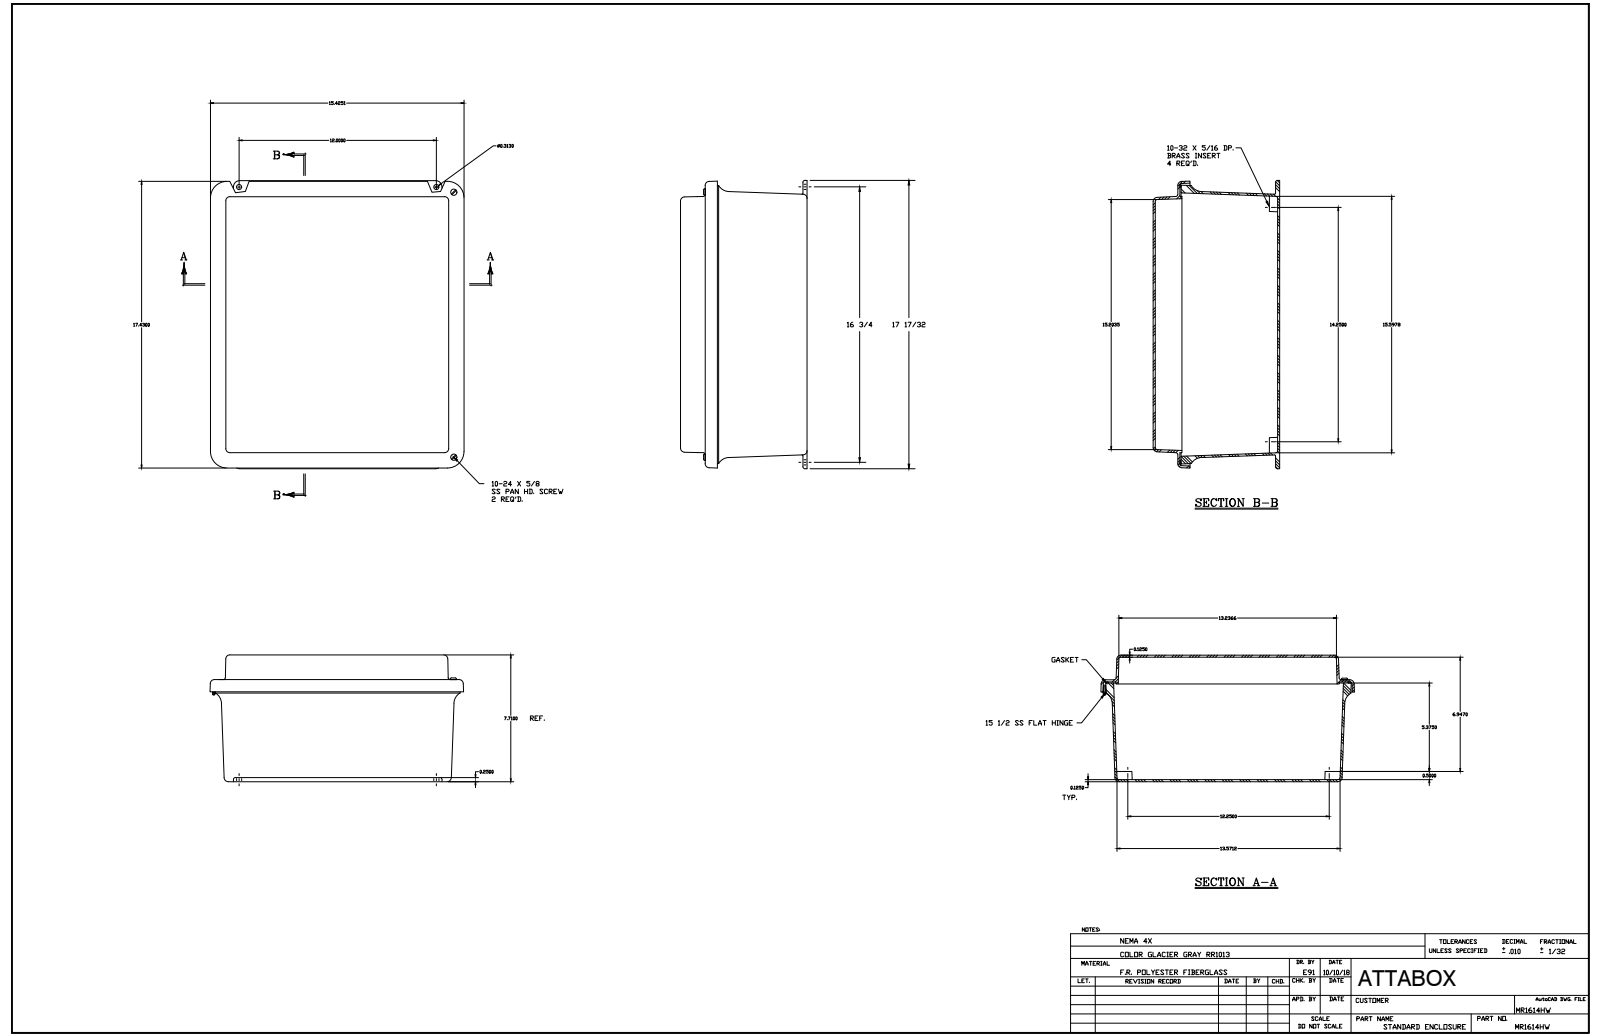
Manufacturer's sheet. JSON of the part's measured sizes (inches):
{"part_name": "MR1614HW", "step_written_by": "SolidWorks 2018 (AUTOMOTIVE_DESIGN)", "units": "inches", "bodies": {"solids": 24, "faces": 965, "planar": 364, "cylindrical": 370, "other": 231}, "overall_size": [17.531, 15.453, 7.697], "volume_in3": 146.7, "surface_area_in2": 2101, "round_holes": [[0.131, 10], [0.14, 10], [0.152, 8], [0.156, 4], [0.218, 4], [0.145, 2], [0.085, 1]], "round_bosses_or_shafts": [[0.25, 10], [0.27, 6], [0.125, 5], [0.125, 5], [0.19, 2], [0.156, 2], [0.155, 1], [0.085, 1]], "partial_cylinders_radius": [[0.031, 20], [0.125, 20], [0.25, 20], [0.2, 4], [0.297, 4], [0.375, 4], [0.75, 4], [0.063, 2]], "face_to_face_distances": [0.125, 0.125, 7.447, 7.697, 7.572, 7.572, 1.502, 5.945, 6.07, 1.627], "hole_center_spacings": [3.75, 7.5, 11.25, 0.25, 3.5, 1.321, 7.25, 13.22]}
